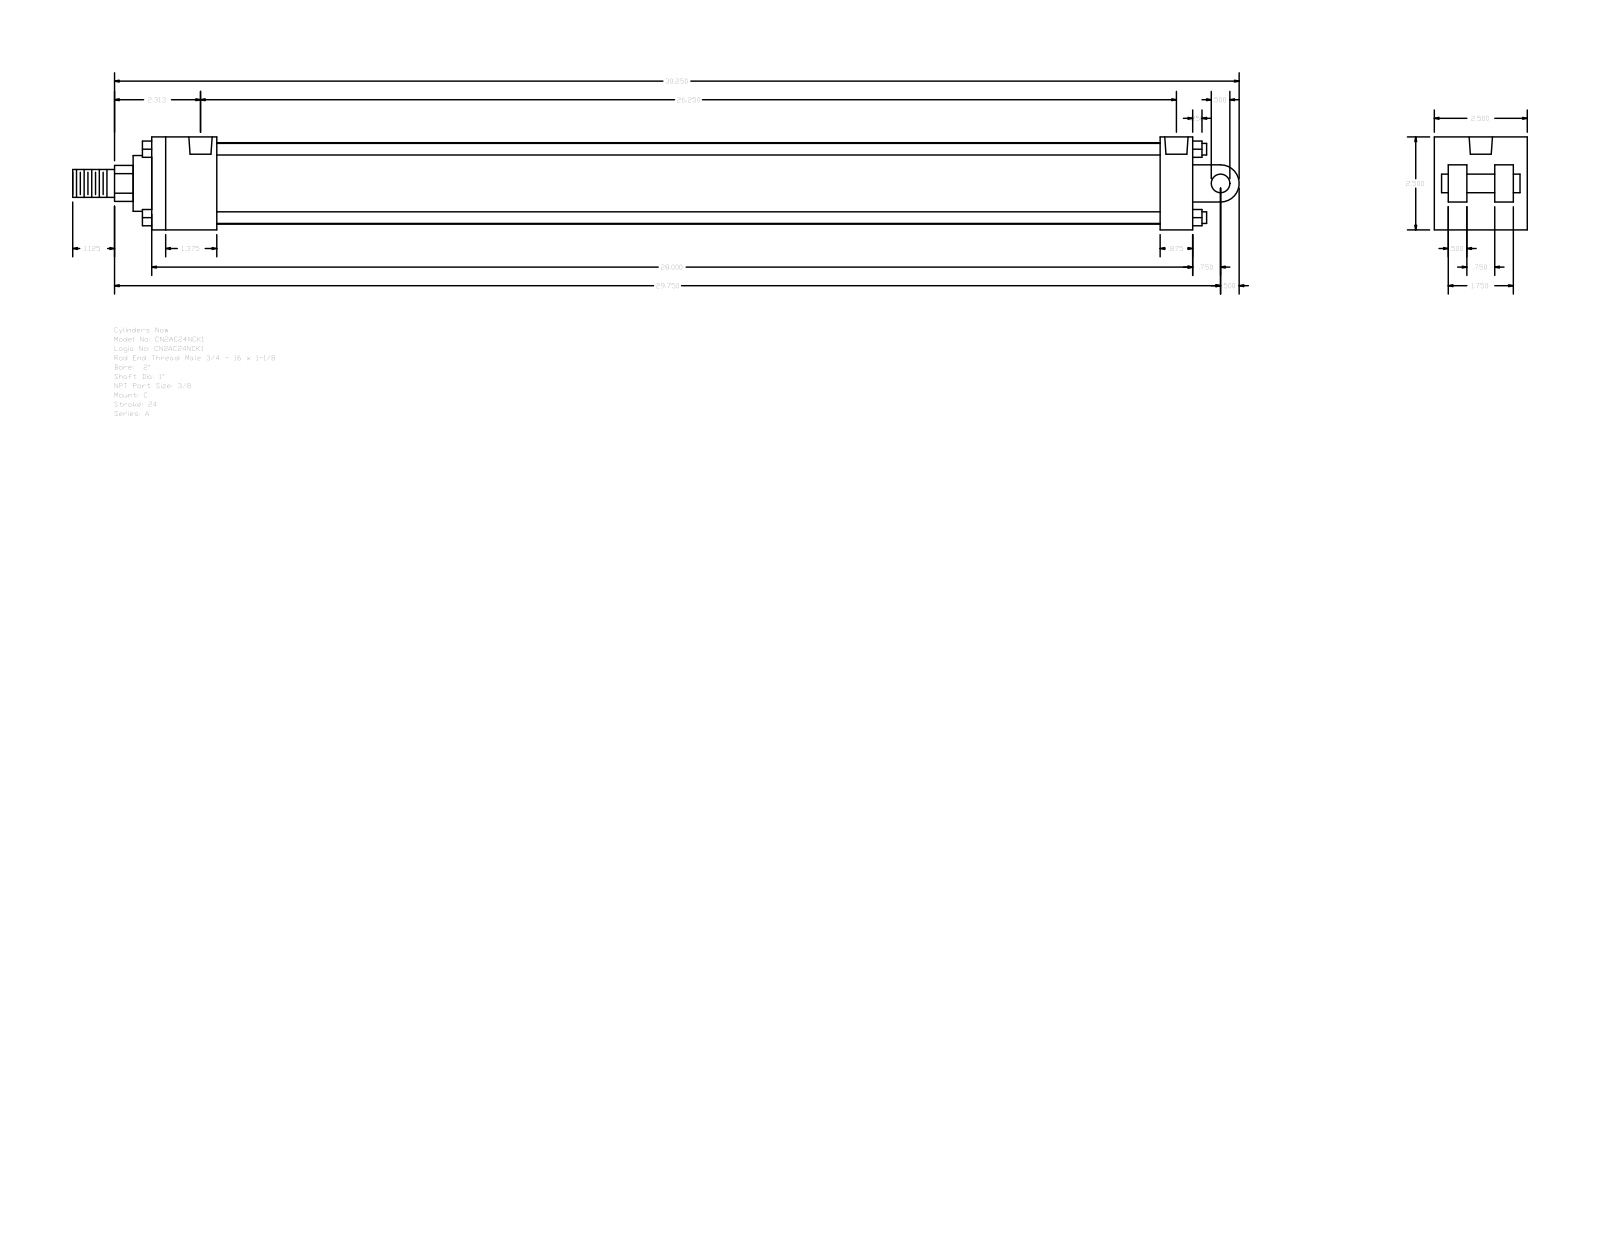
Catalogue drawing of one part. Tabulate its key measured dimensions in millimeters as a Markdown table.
| quantity | value |
| --- | --- |
| part name | A_C__0200_1 |
| STEP written by | GSSL Pune (CONFIG_CONTROL_DESIGN) |
| units | millimeters |
| bodies | 0 solids, 135 faces (102 planar, 33 cylindrical, 0 other) |
| overall size | 796.92 × 63.5 × 63.5 |
| round holes (diameter × count) | 5.56 × 4, 15.93 × 2 |
| round bosses / shafts (diameter × count) | 7.94 × 4, 55.63 × 1, 38.1 × 1, 25.4 × 1, 19.05 × 1, 12.7 × 1 |
| partial cylindrical surfaces (radius × count) | 12.29 × 1, 12.7 × 1 |
| main face-to-face distances | 63.5, 22.22, 711.2, 44.45, 12.7, 9.52, 666.75, 688.98, 644.53, 53.98 |
| hole center spacings | 661.18, 1.59, 3.98, 662.77, 665.16, 666.75 |
